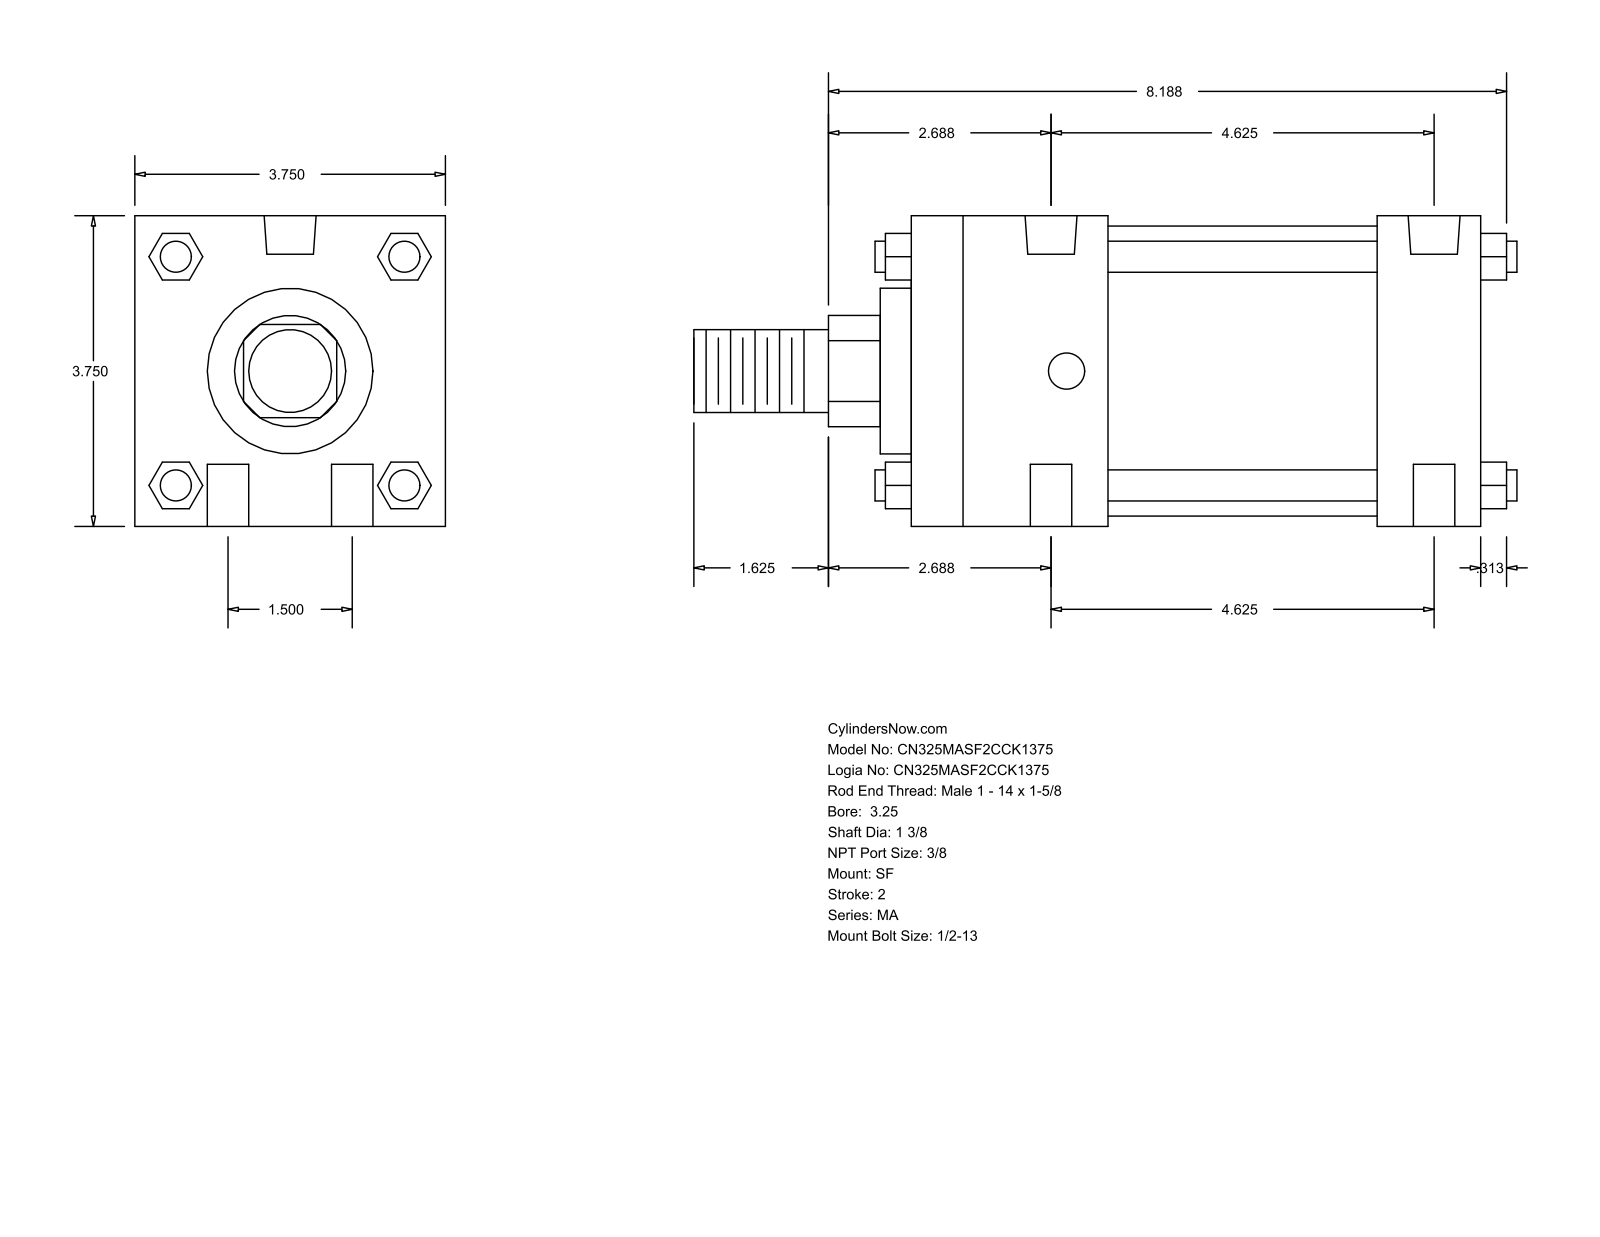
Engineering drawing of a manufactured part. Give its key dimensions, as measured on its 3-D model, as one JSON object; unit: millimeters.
{"part_name": "MA_SF__0325_1.375", "step_written_by": "GSSL Pune (CONFIG_CONTROL_DESIGN)", "units": "millimeters", "bodies": {"solids": 0, "faces": 124, "planar": 94, "cylindrical": 30, "other": 0}, "overall_size": [252.41, 95.25, 95.25], "round_holes": [[12.7, 4], [11.11, 2], [15.93, 2]], "round_bosses_or_shafts": [[9.53, 4], [88.9, 1], [50.8, 1], [34.92, 1], [25.4, 1]], "partial_cylinders_radius": [[17.06, 1]], "face_to_face_distances": [95.24, 174.63, 142.88, 31.75, 60.32, 82.56, 114.31, 9.52, 69.84, 152.4], "hole_center_spacings": [19.05, 119.01, 117.48, 38.1, 123.5, 107.94]}
